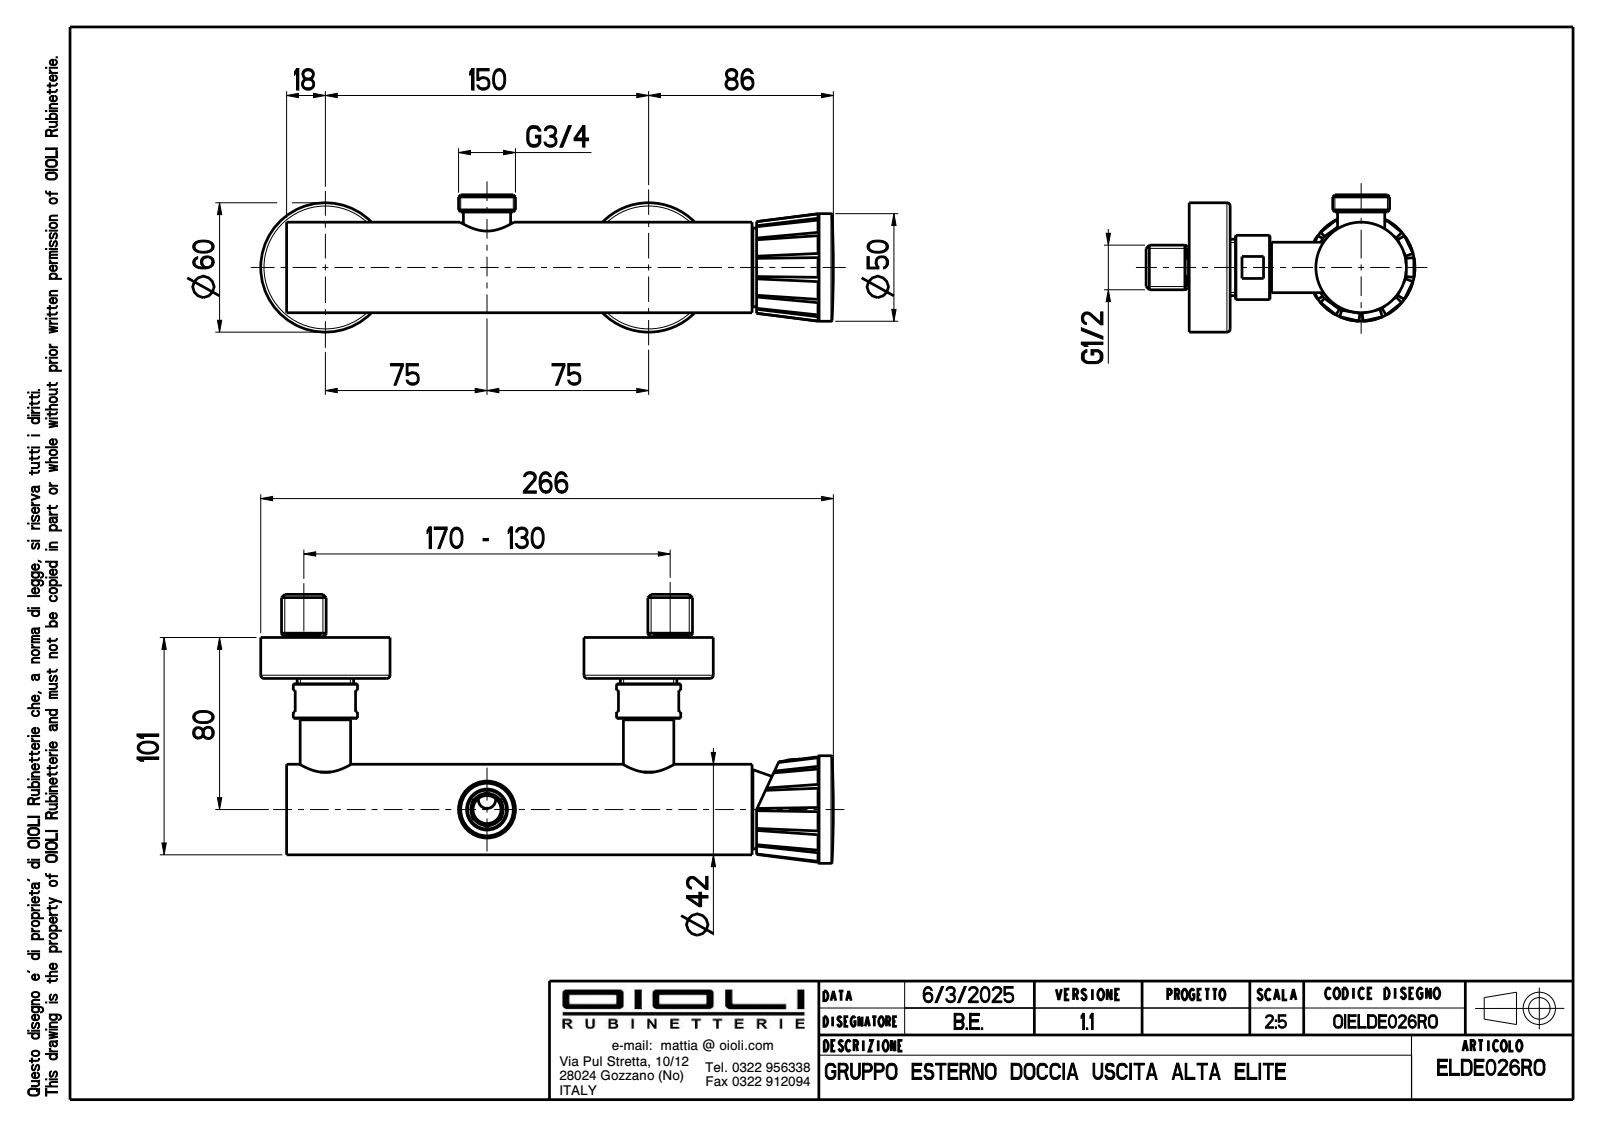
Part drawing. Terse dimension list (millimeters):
name: OIBR00277; OIAQ00285; OIBR00998; OIBR00278 (+8 more)
written by: CREO PARAMETRIC BY PTC INC, 2024493 (CONFIG_CONTROL_DESIGN)
unit: mm
bodies: 15 solids, 679 faces (197 planar, 243 cylindrical, 239 other)
size: 265.72 × 124.75 × 63.7
volume: 323 467 mm³; area: 132 954 mm²
holes: 3× ⌀4, 3× ⌀7, 3× ⌀8, 3× ⌀10, 2× ⌀5, 2× ⌀10.5, 2× ⌀15.5, 2× ⌀16.7, 2× ⌀19, 2× ⌀19.1, 2× ⌀20, 2× ⌀21.8
bosses: 3× ⌀26.4, 2× ⌀60, 2× ⌀29.8, 2× ⌀27.2, 2× ⌀26.2, 2× ⌀23.4, 2× ⌀23.2, 2× ⌀23
rounds: 10× R0.1, 8× R1, 4× R7.5, 2× R0.5
face distances: 0.7, 13, 250.6, 19, 15.5, 5.5, 0.5, 182.5, 68.1, 18.5
hole spacings: 6.28, 10, 13.45, 160, 4.5, 4.61, 4.8, 8.6
